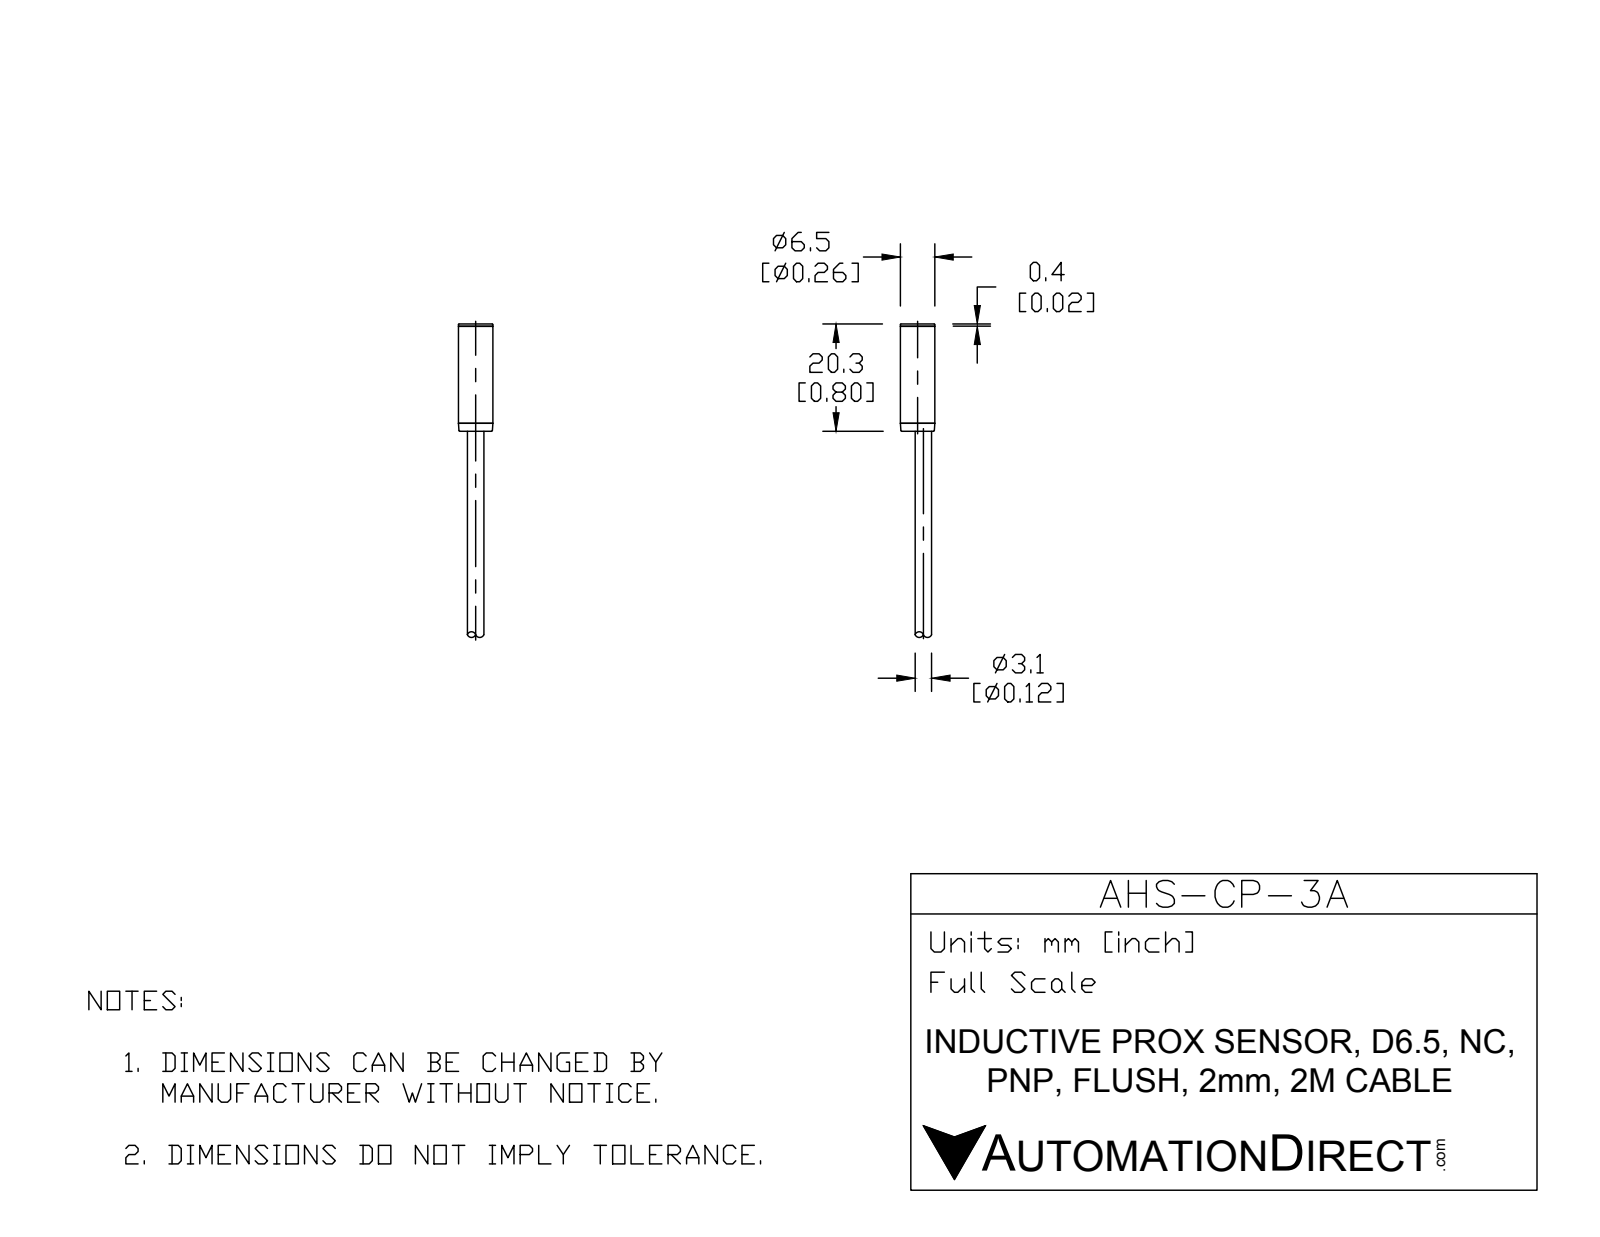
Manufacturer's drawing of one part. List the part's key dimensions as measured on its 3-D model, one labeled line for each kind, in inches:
Part name (STEP PRODUCT): AHS-CP-3A
STEP written by: SolidWorks 2015 (CONFIG_CONTROL_DESIGN)
Units: inches
Bodies: 2 solids, 17 faces (5 planar, 6 cylindrical, 6 other)
Overall size (bounding box): 2.768 × 0.256 × 0.256
Volume: 0.064 in³ · Surface area: 1.52 in²
Round bosses / shafts (diameter × count): ⌀0.256 ×1, ⌀0.122 ×1
Main face-to-face distances: 0.799, 1.969, 2.768, 2.752, 0.783, 0.016
